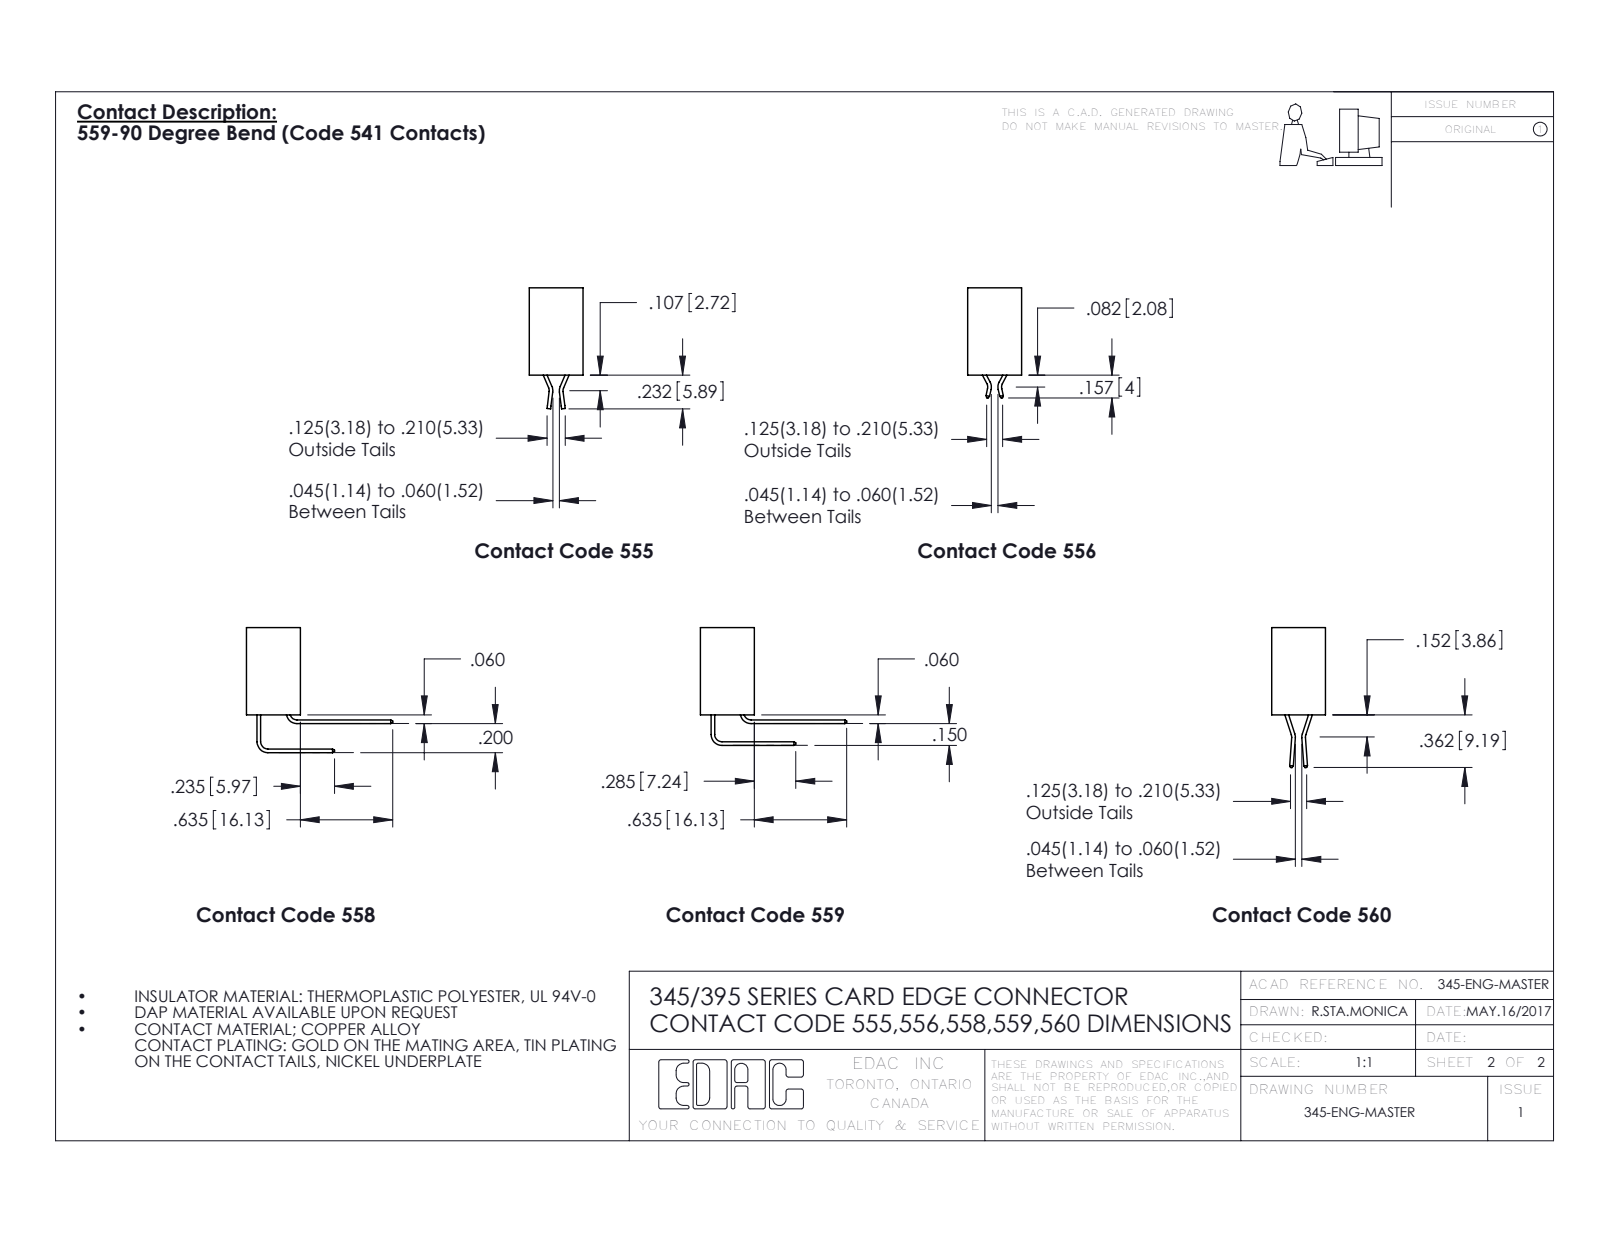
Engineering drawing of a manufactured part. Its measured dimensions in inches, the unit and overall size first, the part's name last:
Units: inches
Overall size (bounding box): 6.56 × 0.762 × 0.37
Round holes (diameter × count): ⌀0.064 ×1
Partial cylindrical surfaces — rounded edges, fillets, slot ends (radius × count): R0.006 ×189, R0.01 ×22, R0.007 ×6, R0.031 ×6, R0.026 ×3, R0.014 ×2, R0.019 ×2, R0.022 ×2
Main face-to-face distances: 0.298, 0.072, 0.2, 0.37, 0.098, 0.272, 0.025, 0.225, 0.072, 0.175
Volume: 1.026 in³ · Surface area: 38.83 in²
Bodies: 127 solids, 6922 faces (4990 planar, 1932 cylindrical, 0 other)
Part name (STEP PRODUCT): 345 Part_No Mounting Lugs; 395-126-524-201; 345-292-001_345-293-124
STEP written by: SolidWorks 2016 (CONFIG_CONTROL_DESIGN)
